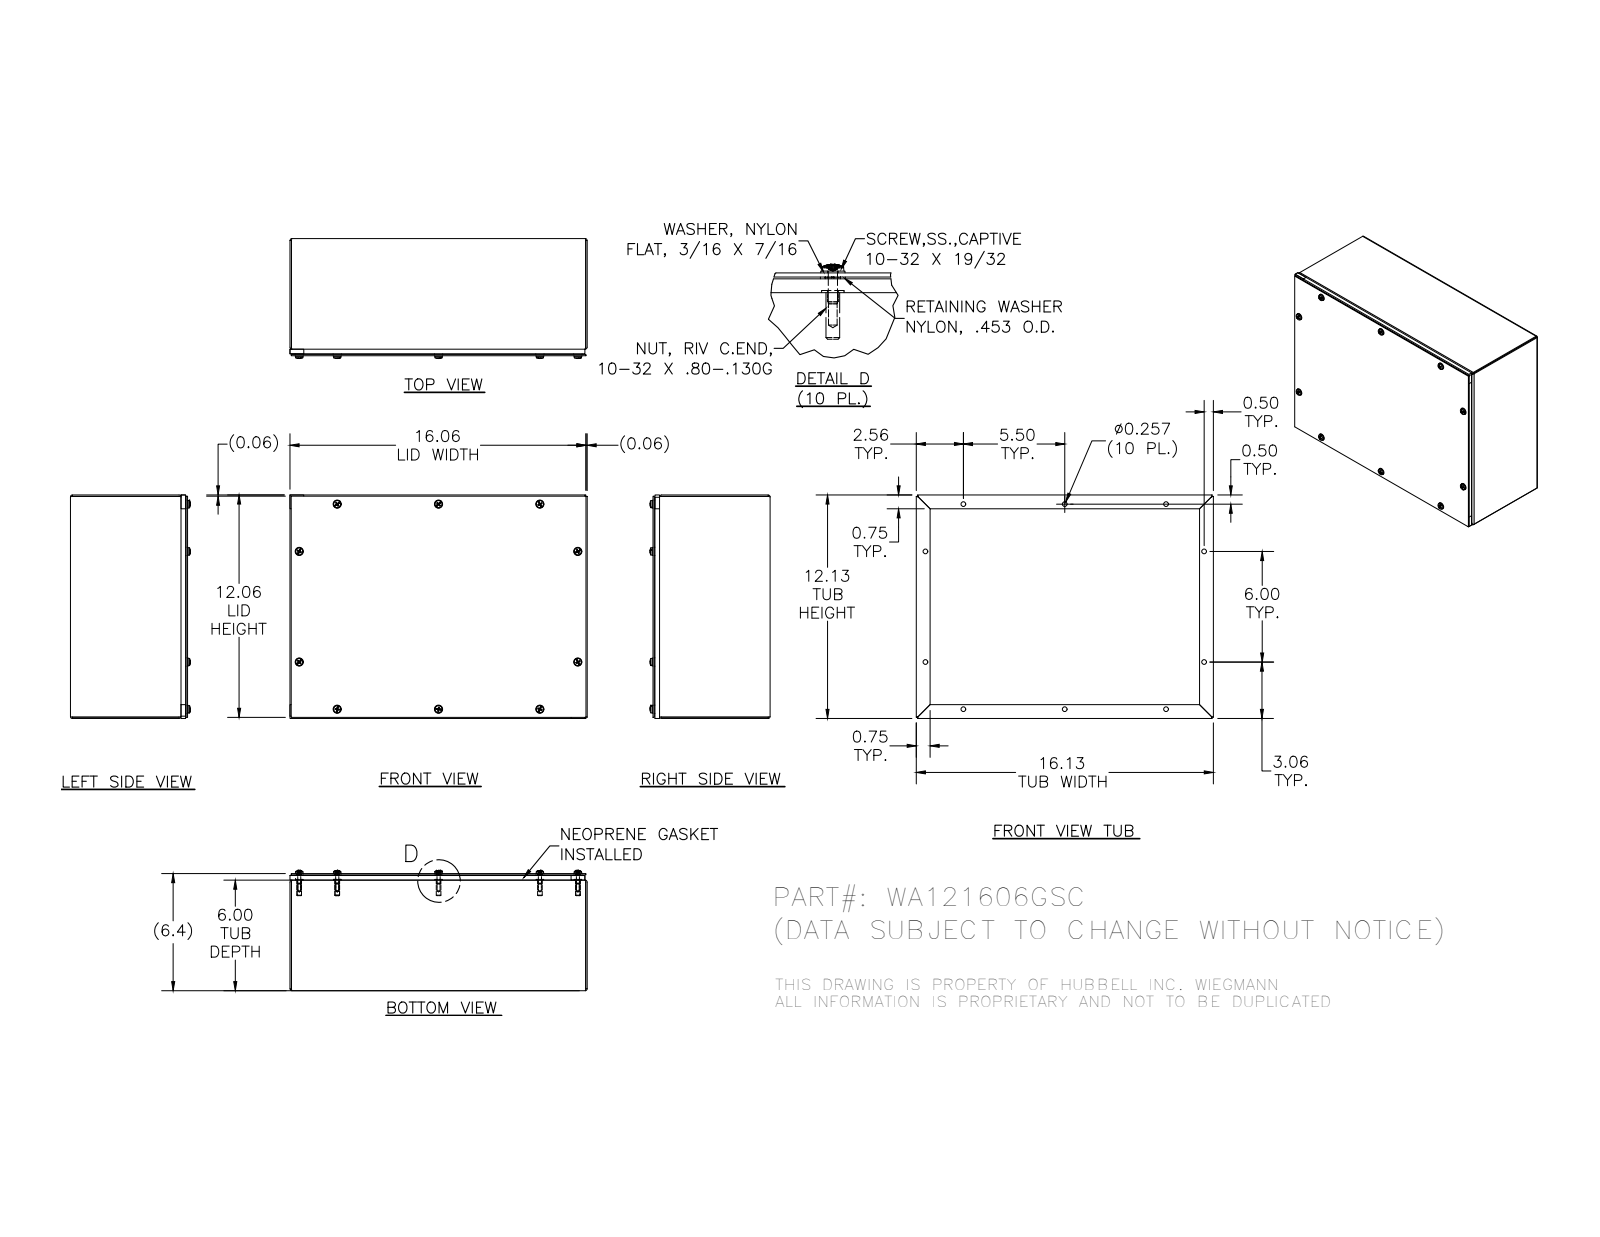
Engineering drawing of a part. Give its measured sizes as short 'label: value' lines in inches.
name: 34984; 37210; 39035; WA121606GSC (+3 more)
written by: SolidWorks 2014 (AUTOMOTIVE_DESIGN)
unit: in
bodies: 45 solids, 1064 faces (502 planar, 276 cylindrical, 286 other)
size: 16.125 × 12.125 × 6.511
volume: 64.39 in³; area: 1 629 in²
holes: 10× ⌀0.188, 10× ⌀0.257, 10× ⌀0.278, 10× ⌀0.281, 9× ⌀0.156, 9× ⌀0.196
bosses: 10× ⌀0.453, 10× ⌀0.437, 10× ⌀0.167, 9× ⌀0.406, 9× ⌀0.248
rounds: 10× R0.089, 8× R0.031, 8× R0.105
face distances: 0.074, 6.282, 6.356, 6.208, 12.051, 16.051, 0.356, 5.926, 12.125, 11.977
hole spacings: 5.5, 11.424, 3.289, 6, 7.985, 8.807, 11, 13.311
